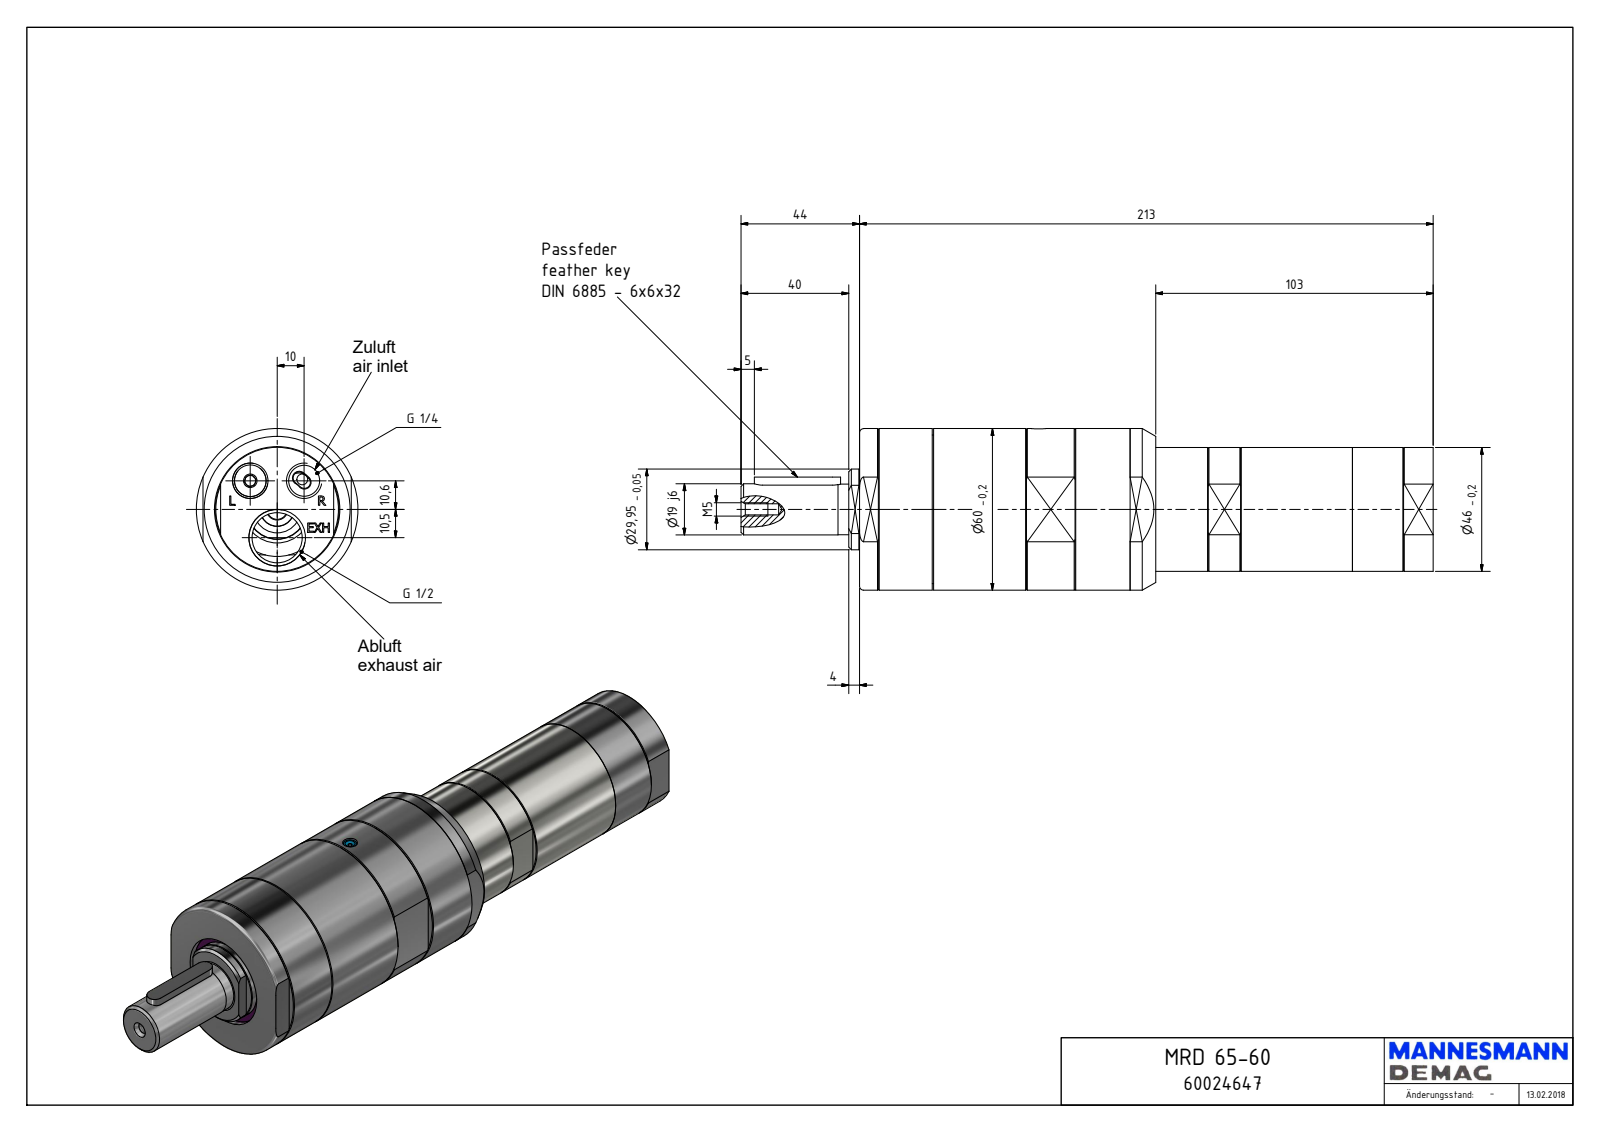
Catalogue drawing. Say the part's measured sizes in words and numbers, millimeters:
The part is named "MRD 65-60_60024647". Its 3-D file was written by "Autodesk Inventor 2018 (AUTOMOTIVE_DESIGN)". It is 1 solid with 230 faces: 129 planar, 52 cylindrical and 49 other. Overall it measures 257 by 60 by 60 millimeters. Its volume is 486 435 cubic millimeters and its surface area 49 374 square millimeters. Round holes: 2 of diameter 4, 1 of diameter 1.55, 1 of diameter 4.13, 1 of diameter 5.5, 1 of diameter 11.45, 1 of diameter 18.63, 1 of diameter 35, 1 of diameter 46.5, 1 of diameter 55.38. Round bosses or shafts: 1 of diameter 60, 1 of diameter 55.18, 1 of diameter 46, 1 of diameter 33.34, 1 of diameter 29.95, 1 of diameter 19, 1 of diameter 18.8, 1 of diameter 5. Partial cylindrical surfaces (rounded edges, fillets, slot ends): 4 of radius 2.5, 2 of radius 3, 2 of radius 5, 1 of radius 5.72, 1 of radius 16.75, 1 of radius 19, 1 of radius 25.69. The main face-to-face distances are 213, 6.5, 48.5, 55, 103, 110, 185.5, 27.5, 82.5, 42. The hole center spacings are 14.57, 23.35, 10.5, 20.
